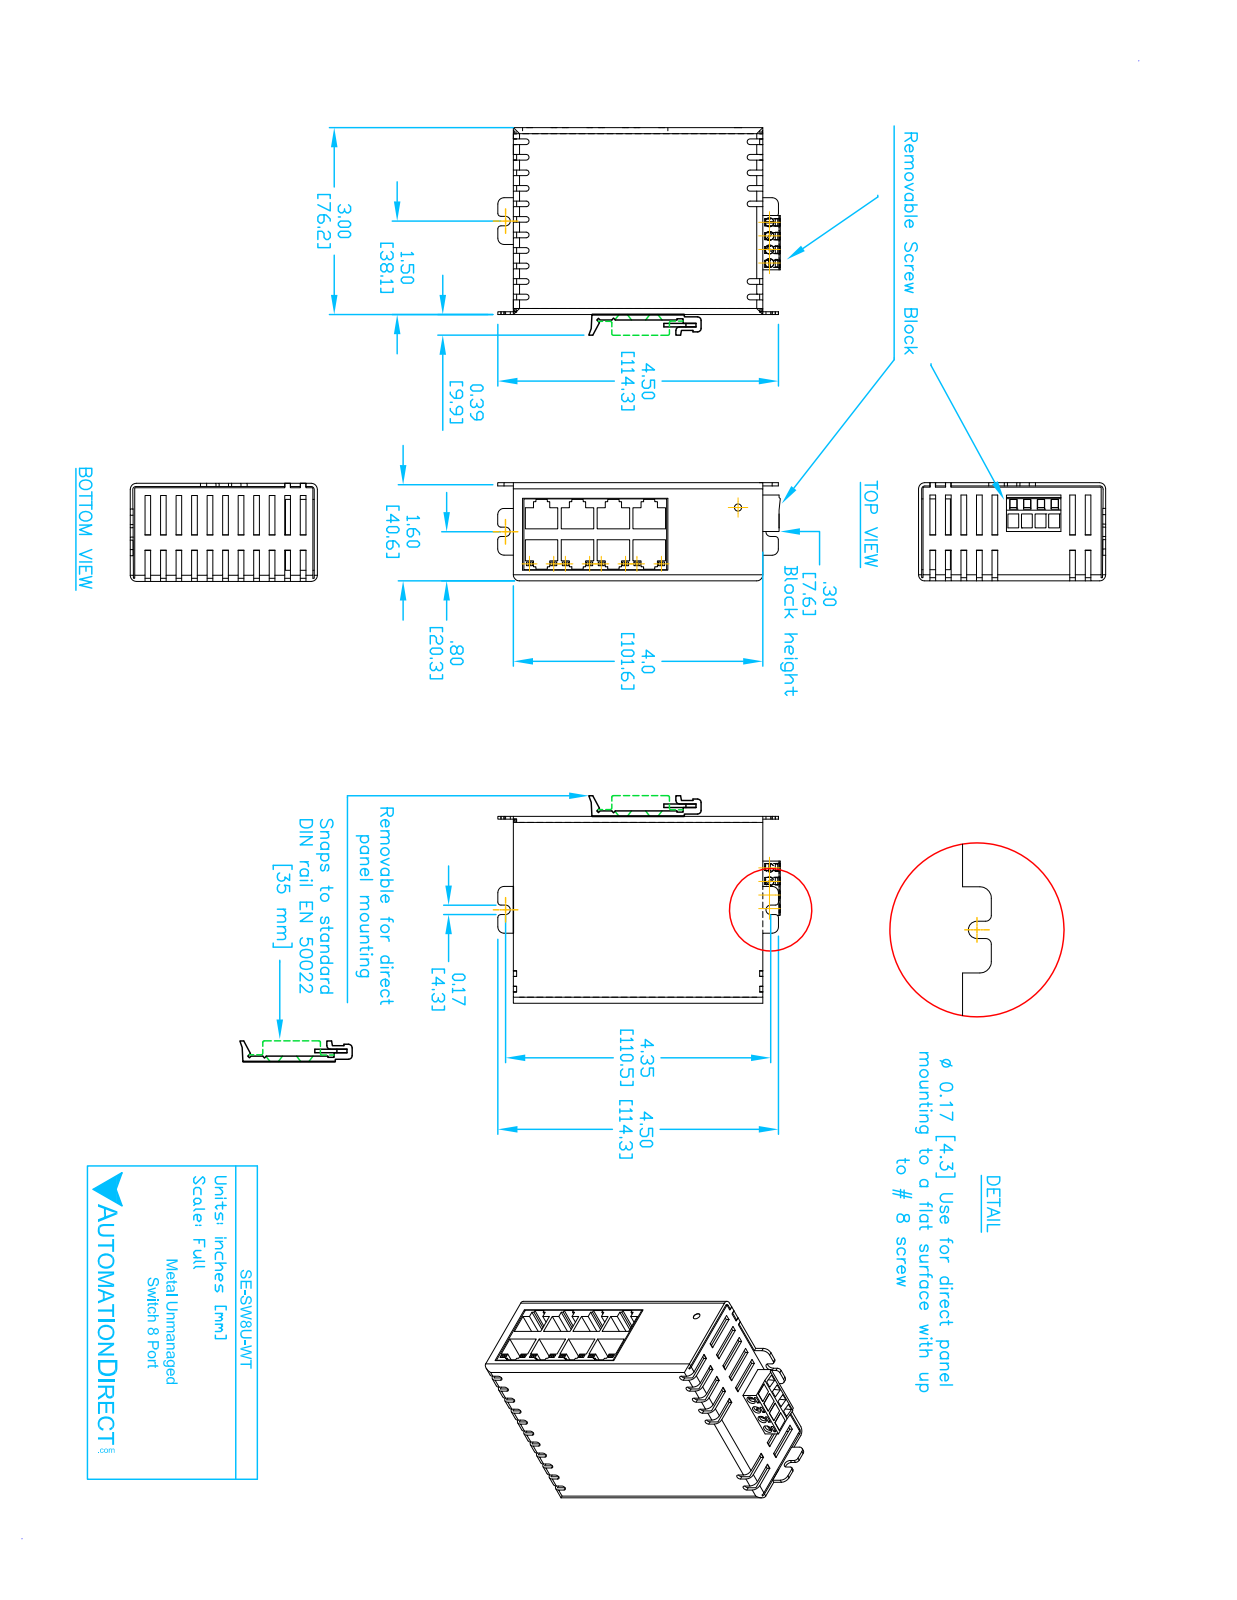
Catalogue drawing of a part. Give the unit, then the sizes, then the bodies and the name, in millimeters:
Units: millimetres
Overall size (bounding box): 115.89 × 84.91 × 40.6
Round holes (diameter × count): ⌀3.81 ×4
Partial cylindrical surfaces — rounded edges, fillets, slot ends (radius × count): R1.27 ×8, R2.54 ×8, R1 ×5, R1.45 ×3, R0.5 ×2, R1.91 ×2, R1.91 ×2
Main face-to-face distances: 0.5, 40.1, 40.6, 39.6, 75.7, 101.1, 76.2, 100.6, 101.6, 76.45
Hole centre spacings: 5.08, 10.16, 15.24
Volume: 36 313 mm³ · Surface area: 77 923 mm²
Bodies: 29 solids, 477 faces (384 planar, 38 cylindrical, 55 other)
Part name (STEP PRODUCT): SE-SW8U-WT
STEP written by: SolidWorks 2011 (AUTOMOTIVE_DESIGN)
